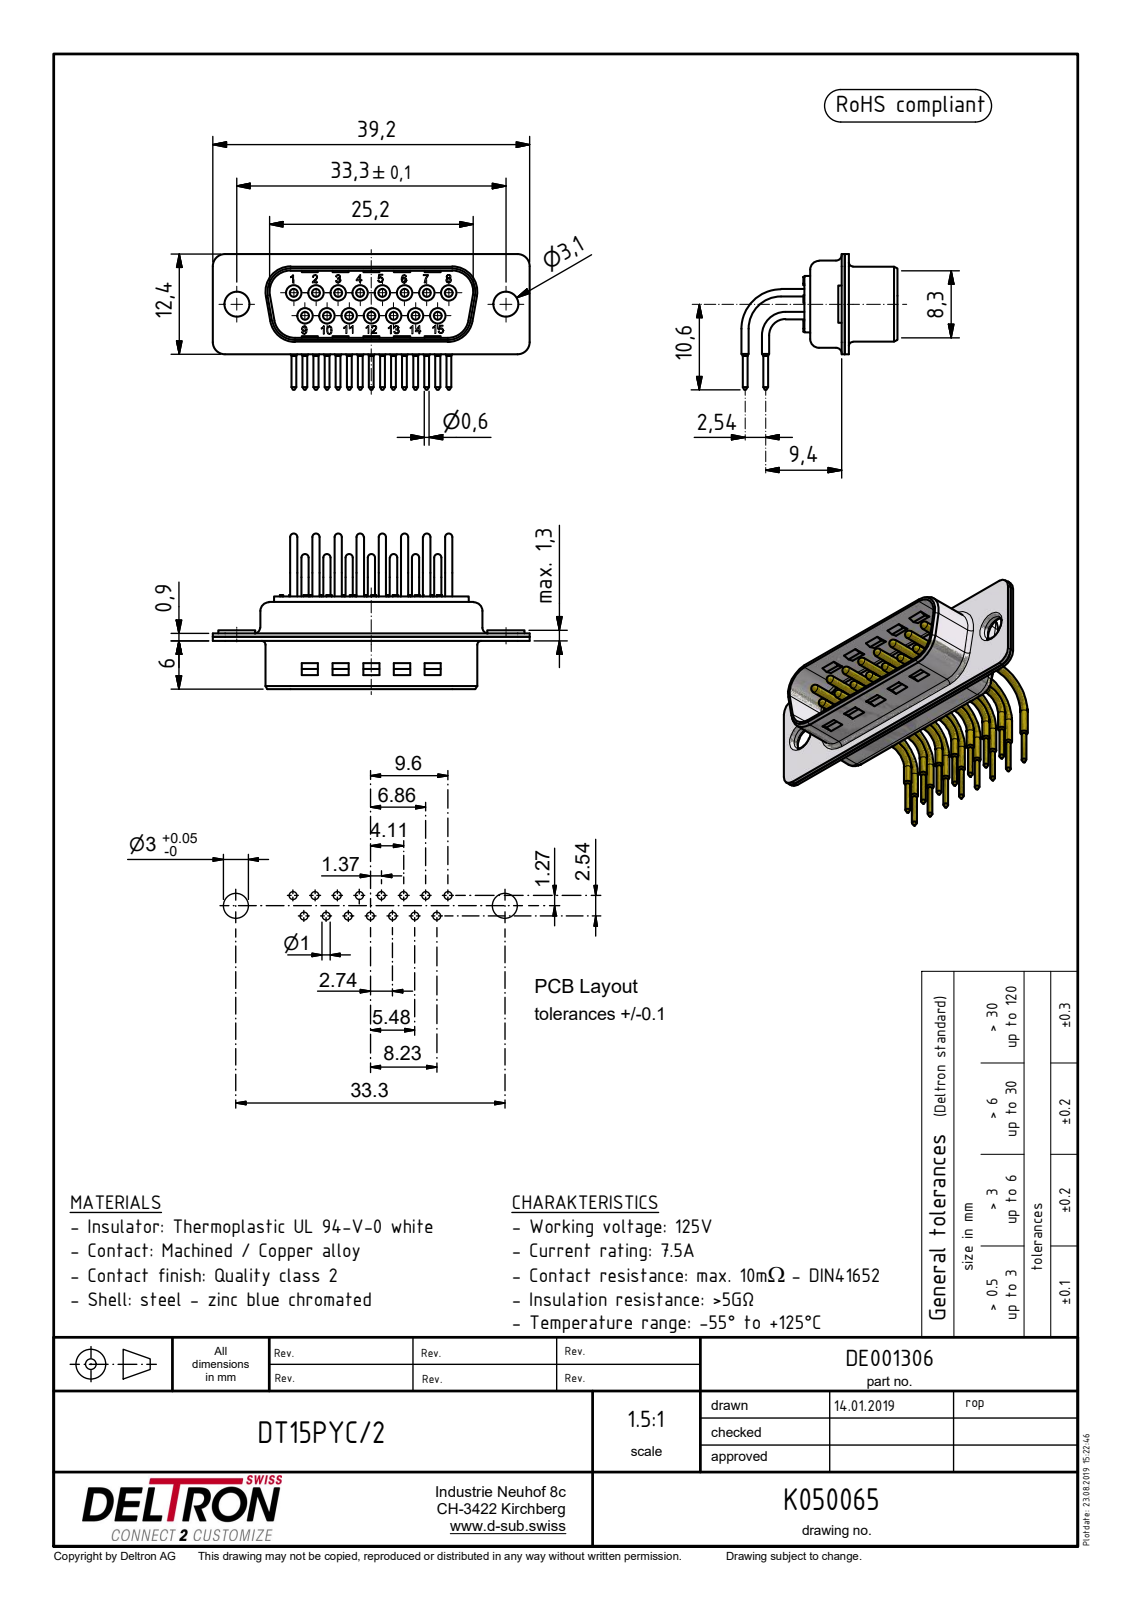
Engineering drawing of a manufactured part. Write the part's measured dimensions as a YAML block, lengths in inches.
part_name: "K050065; N00403_BG; R+B00913_BG; R+B00914_BG (+2 more)"
step_written_by: "Autodesk Inventor 2018 (AUTOMOTIVE_DESIGN)"
units: inches
bodies: {solids: 18, faces: 2655, planar: 1546, cylindrical: 806, other: 303}
overall_size: [1.543, 0.759, 0.661]
volume: 0.105
surface_area: 7.8
round_holes:
  - {diameter: 0.076, count: 15}
  - {diameter: 0.091, count: 15}
  - {diameter: 0.013, count: 2}
  - {diameter: 0.122, count: 2}
  - {diameter: 0.16, count: 2}
  - {diameter: 0.009, count: 1}
  - {diameter: 0.011, count: 1}
round_bosses_or_shafts:
  - {diameter: 0.035, count: 30}
  - {diameter: 0.077, count: 15}
  - {diameter: 0.076, count: 15}
  - {diameter: 0.063, count: 15}
  - {diameter: 0.063, count: 15}
  - {diameter: 0.039, count: 15}
  - {diameter: 0.024, count: 15}
  - {diameter: 0.181, count: 2}
partial_cylinders:
  - {radius: 0.042, count: 15}
  - {radius: 0.079, count: 12}
  - {radius: 0.01, count: 8}
  - {radius: 0.028, count: 8}
  - {radius: 0.039, count: 8}
  - {radius: 0.043, count: 8}
  - {radius: 0.02, count: 4}
  - {radius: 0.047, count: 4}
face_to_face_distances: [0.02, 0.016, 0.346, 0.026, 0.031, 0.327, 0.035, 0.024, 0.352, 0.372]
hole_center_spacings: [0.124, 0.108, 0.197, 0.216, 0.292, 0.324, 0.394, 0.431]
